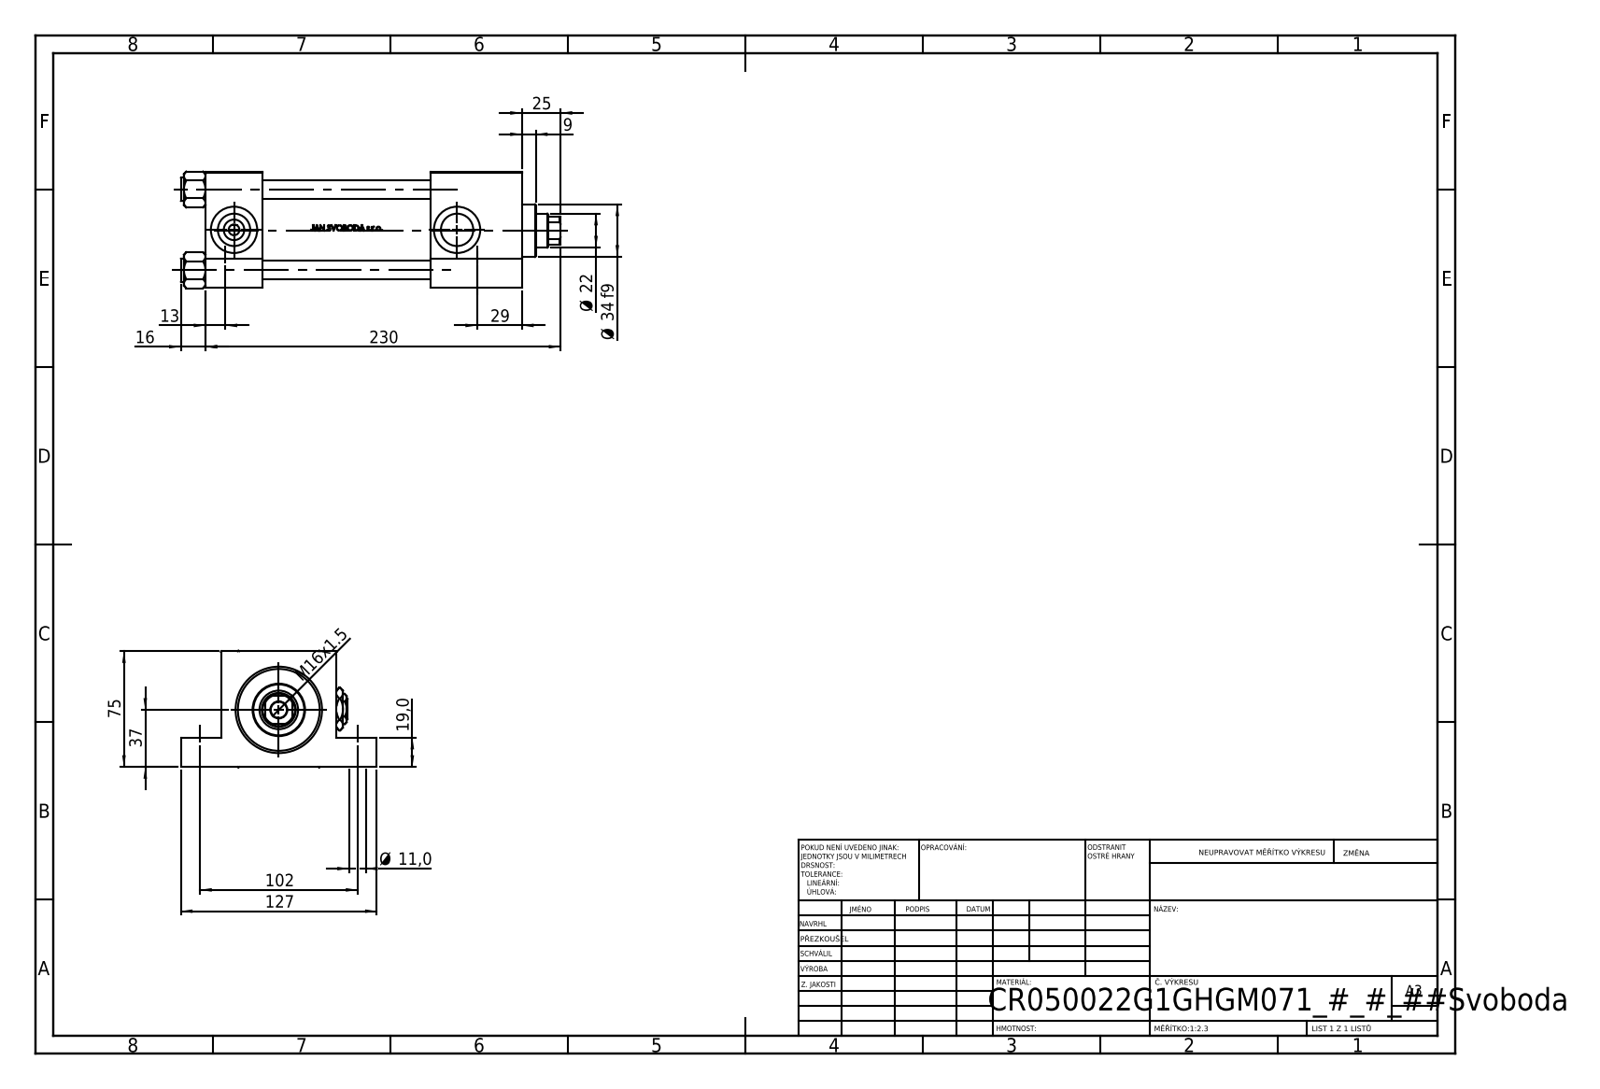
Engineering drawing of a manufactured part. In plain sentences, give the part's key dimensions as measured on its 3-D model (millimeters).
The part is named "V215_VC_A; NUT_M5_G; V215CR_VCP_G; V215CR_G_TYCINKA (+2 more)". Its 3-D file was written by "SolidWorks 2019 (CONFIG_CONTROL_DESIGN)". It is 12 solids with 1134 faces: 454 planar, 128 cylindrical and 552 other. Overall it measures 246 by 127 by 75.54 millimeters. Its volume is 820 337 cubic millimeters and its surface area 189 503 square millimeters. Round holes: 4 of diameter 11, 4 of diameter 12, 2 of diameter 7, 2 of diameter 20.96, 2 of diameter 30, 1 of diameter 10.5, 1 of diameter 22, 1 of diameter 25, 1 of diameter 41, 1 of diameter 50, 1 of diameter 53. Round bosses or shafts: 4 of diameter 15, 1 of diameter 56, 1 of diameter 34. Partial cylindrical surfaces (rounded edges, fillets, slot ends): 1 of radius 10.5. The main face-to-face distances are 75, 37, 205, 168, 19, 56, 146, 109, 59, 26. The hole center spacings are 52.3, 36.63, 37.34, 73.96, 102, 163, 192.28, 144.5.
